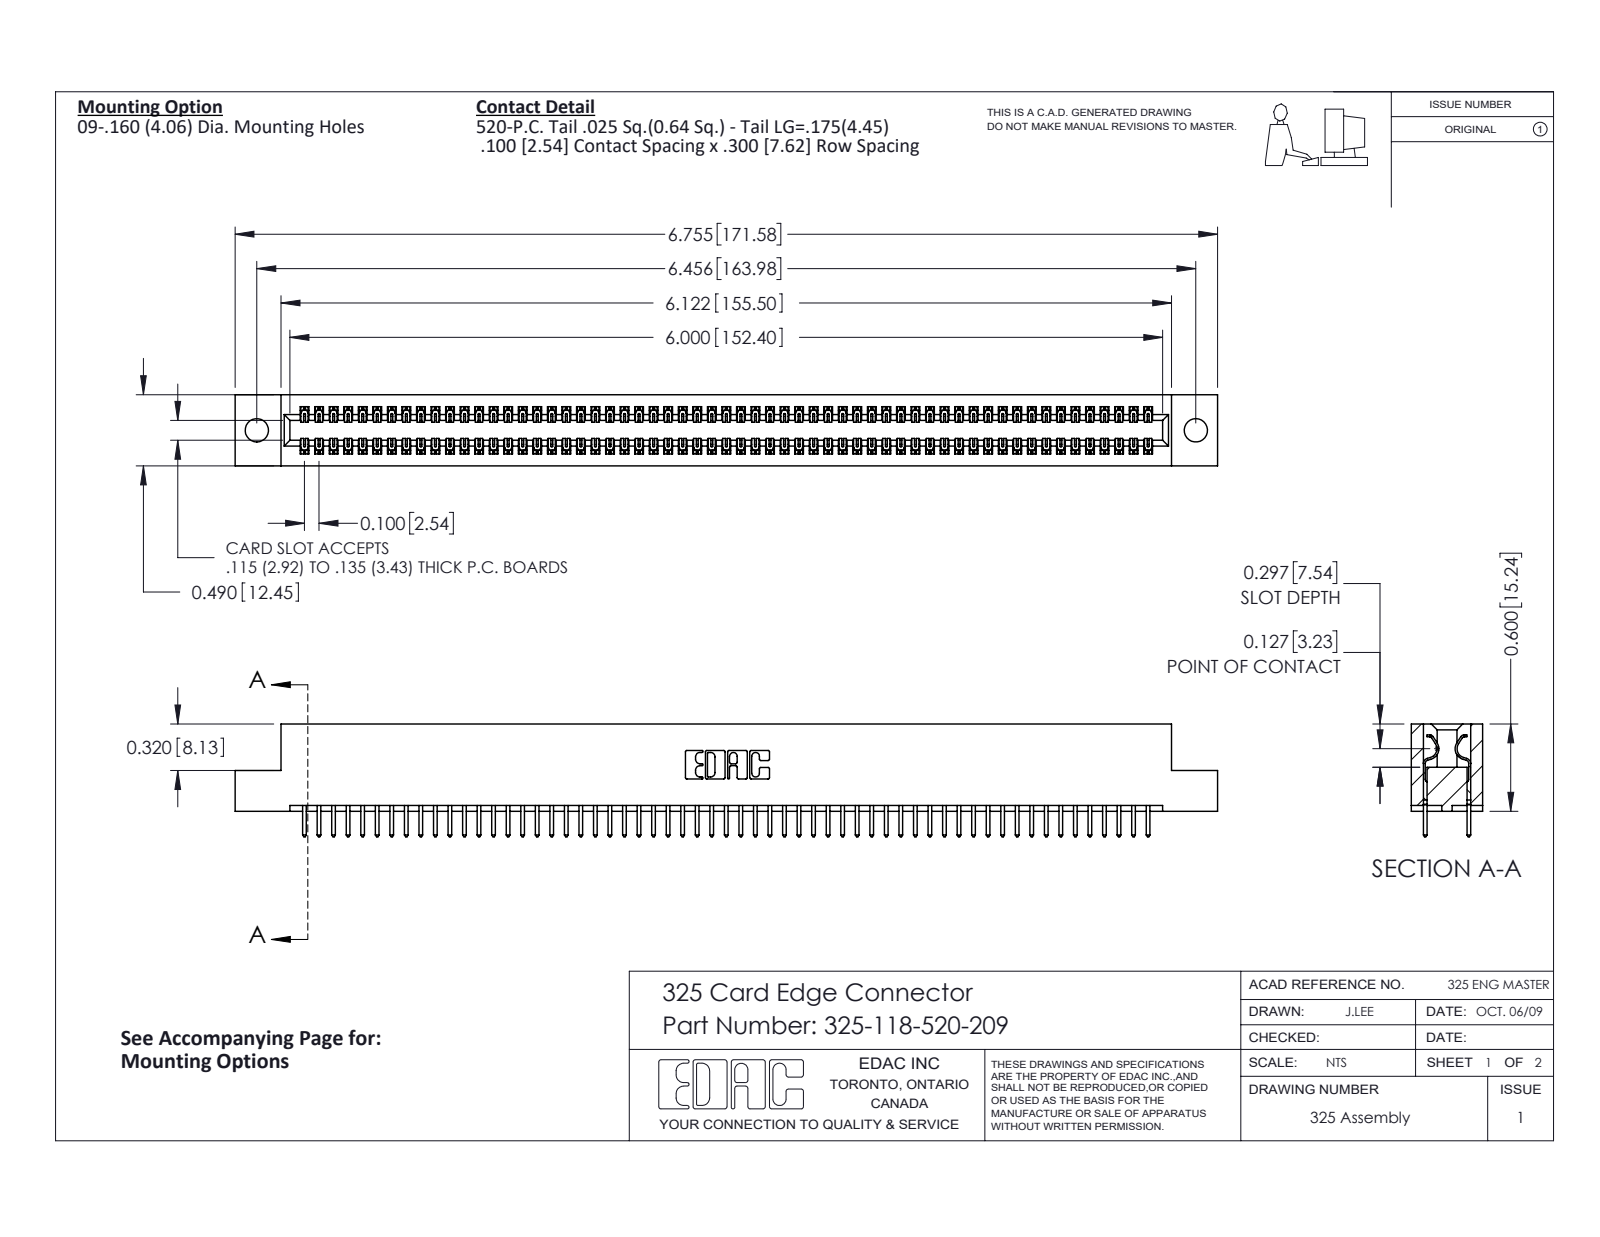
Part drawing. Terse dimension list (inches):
name: 325-118-520-209; 325-292-001_325-293-120; 325 Part_.160 TH
written by: SolidWorks 2016 (CONFIG_CONTROL_DESIGN)
unit: in
bodies: 119 solids, 6250 faces (4318 planar, 1932 cylindrical, 0 other)
size: 6.755 × 0.775 × 0.49
volume: 1.346 in³; area: 41.51 in²
holes: 2× ⌀0.16
rounds: 177× R0.006, 118× R0.01, 22× R0.01, 6× R0.007, 6× R0.031, 3× R0.026, 2× R0.014, 2× R0.022
face distances: 0.083, 0.407, 0.3, 0.49, 0.107, 0.383, 0.025, 0.325, 0.275, 0.56
hole spacings: 6.456
